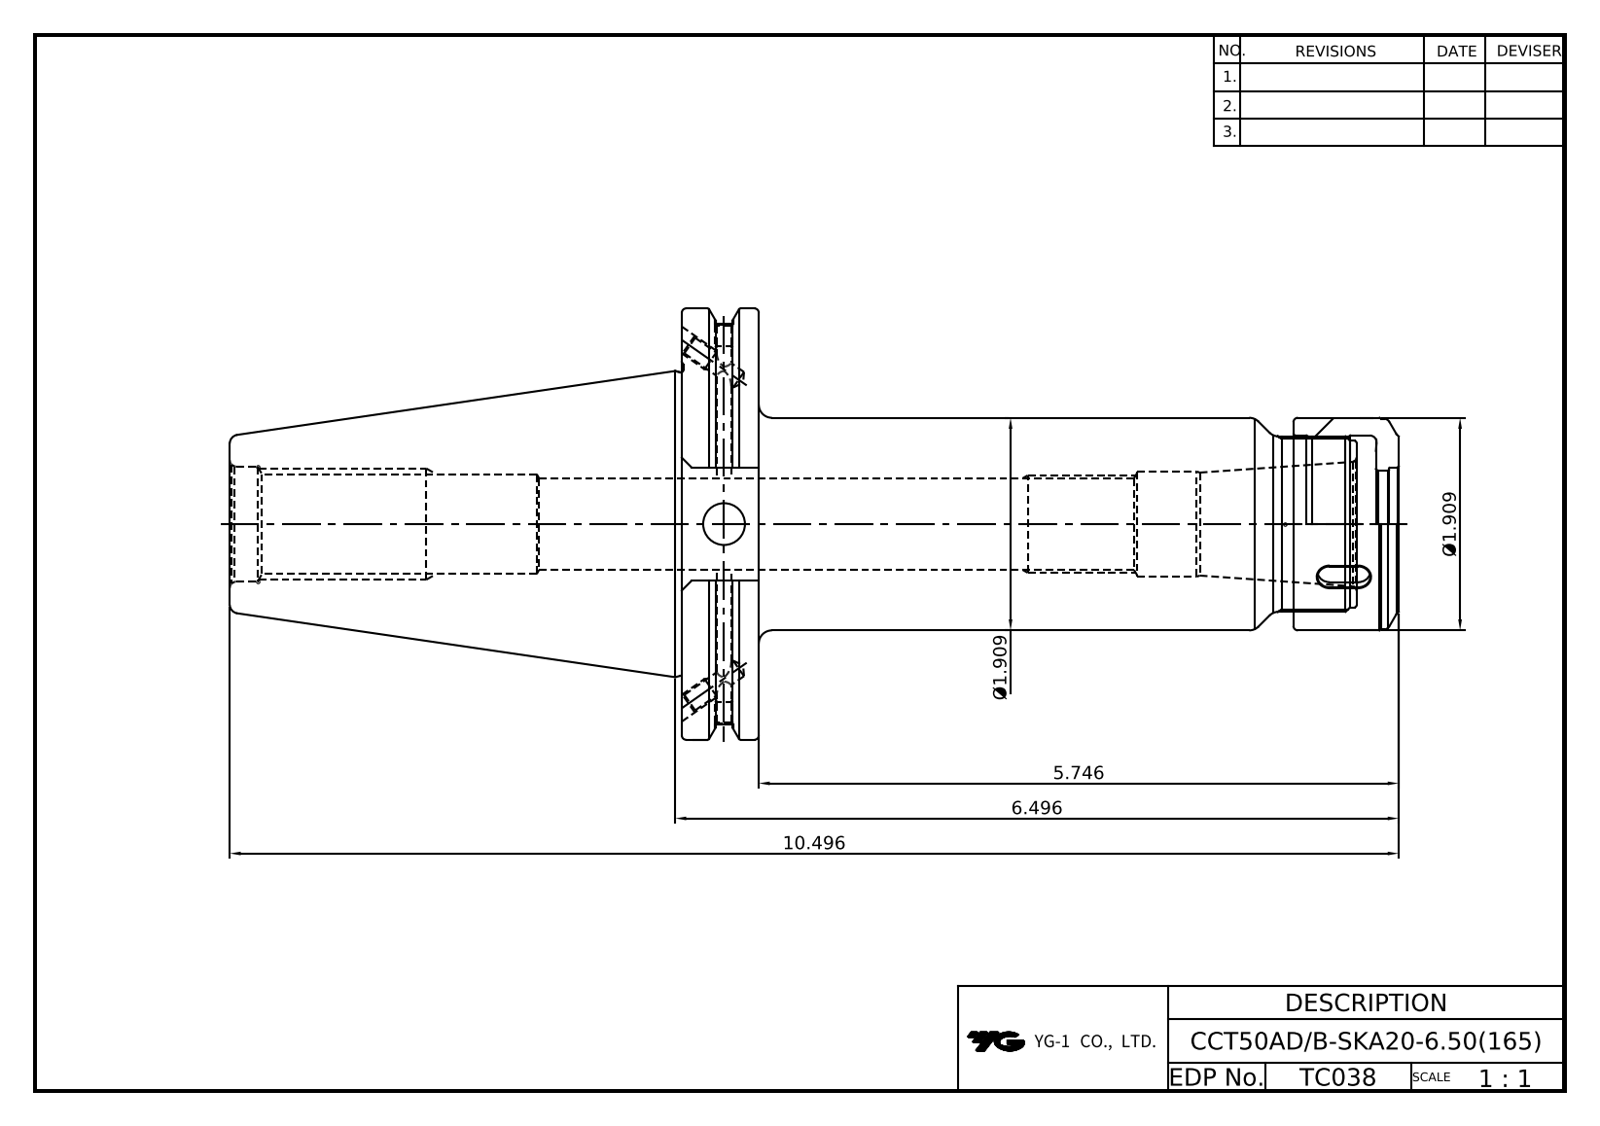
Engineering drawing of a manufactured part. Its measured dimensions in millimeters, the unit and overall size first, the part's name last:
Units: millimetres
Overall size (bounding box): 266.6 × 98.42 × 94.69
Round holes (diameter × count): ⌀3.24 ×2, ⌀4.13 ×2, ⌀4.2 ×2, ⌀5 ×2, ⌀9.53 ×1, ⌀19.18 ×1, ⌀21.97 ×1, ⌀24 ×1, ⌀26.2 ×1, ⌀29.2 ×1, ⌀31 ×1, ⌀38.92 ×1
Round bosses / shafts (diameter × count): ⌀98.42 ×1, ⌀91.29 ×1, ⌀69.25 ×1, ⌀48.5 ×1, ⌀48.1 ×1, ⌀40 ×1, ⌀38 ×1
Main face-to-face distances: 17.55, 103.1, 120.65, 266.6, 163.5, 145.95, 103.5, 73.03, 242.6, 139.5
Volume: 532 721 mm³ · Surface area: 81 920 mm²
Bodies: 2 solids, 170 faces (62 planar, 46 cylindrical, 62 other)
Part name (STEP PRODUCT): LO-CCT50ADB-SKA20-165; SKN20-NUT
STEP written by: Autodesk Inventor 2022 (AUTOMOTIVE_DESIGN)
